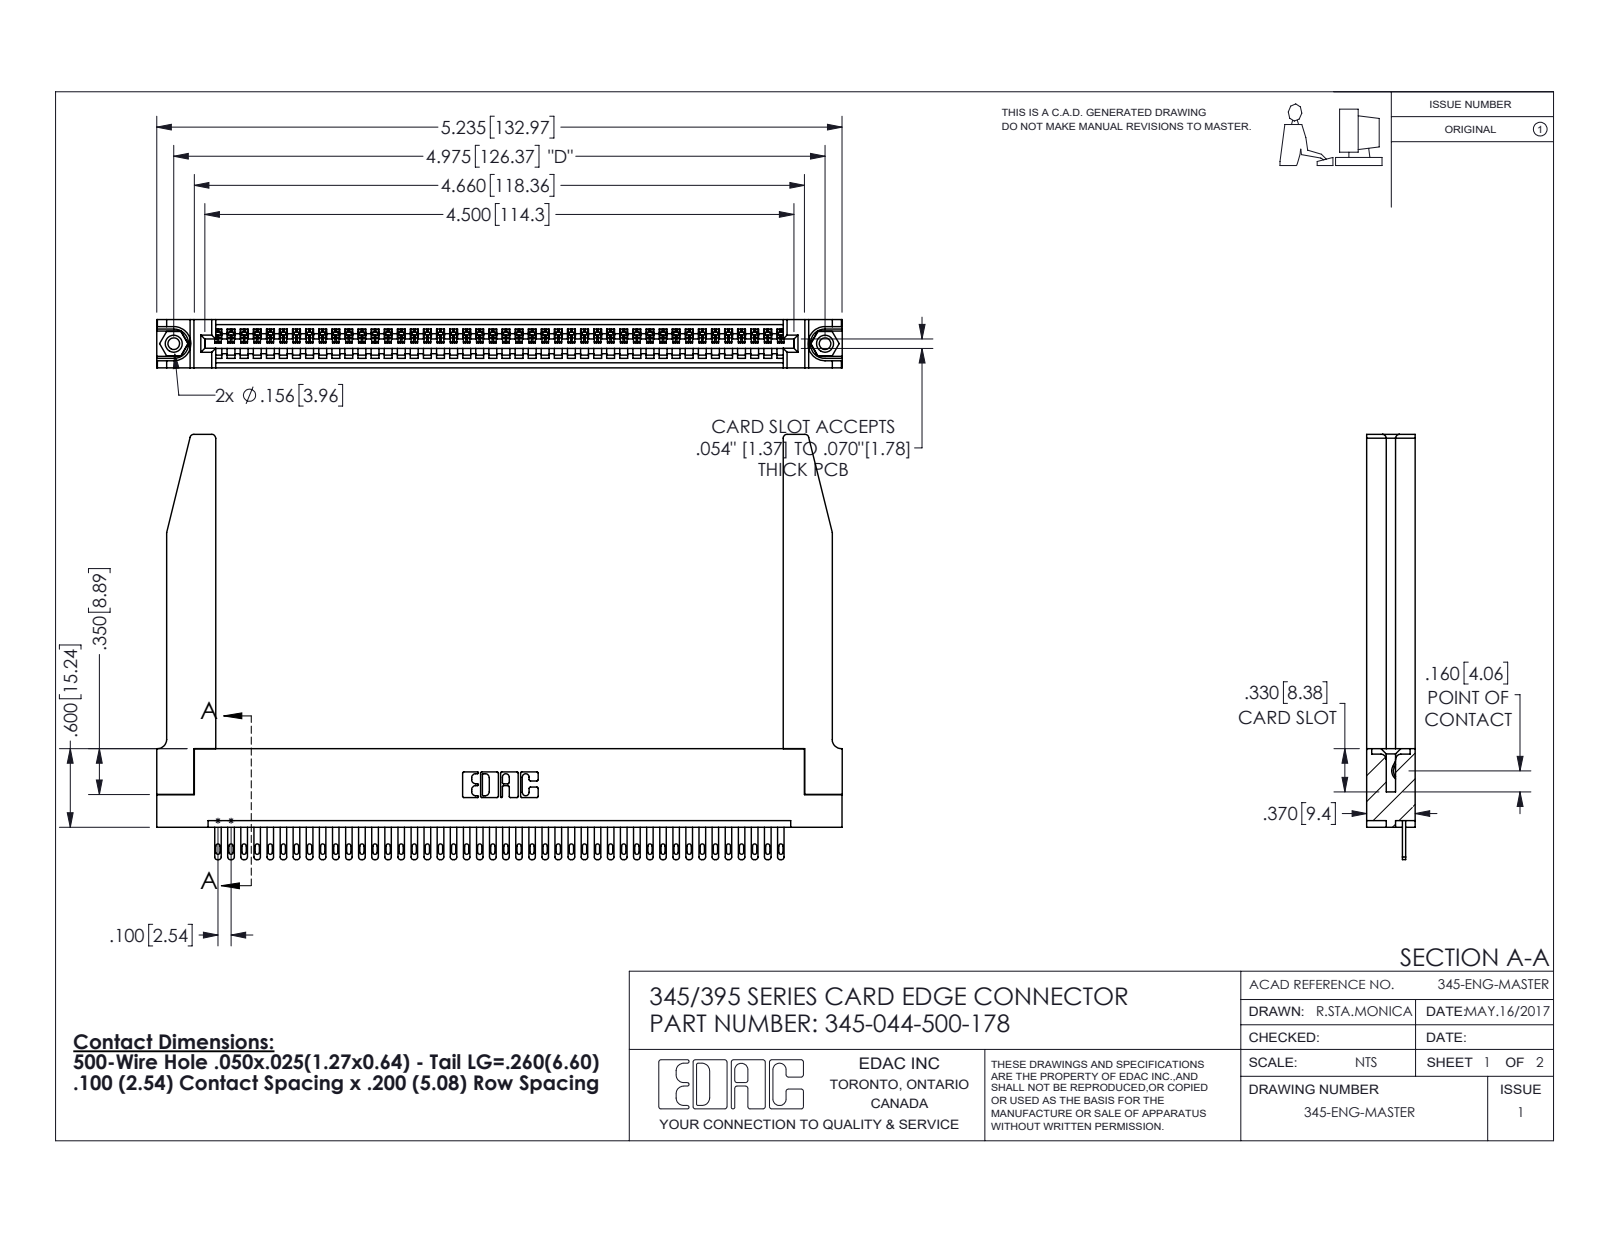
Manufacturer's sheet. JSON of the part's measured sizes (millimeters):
{"part_name": "345-250-001_345-250-001-102; 345 Part_Flush Mounting Lugs - 0.156 Dia-TH; 345-292-001_345-293-100; 345-044-500-178 (+1 more)", "step_written_by": "SolidWorks 2016 (CONFIG_CONTROL_DESIGN)", "units": "millimeters", "bodies": {"solids": 49, "faces": 2736, "planar": 1718, "cylindrical": 966, "other": 52}, "overall_size": [133, 82.5, 9.4], "volume_mm3": 20450, "surface_area_mm2": 23820, "round_holes": [[2.3, 2], [3.2, 2], [4, 2], [1.6, 1]], "round_bosses_or_shafts": [[3.9, 2]], "partial_cylinders_radius": [[0.2, 88], [0.4, 88], [0.5, 88], [0.3, 22], [0.8, 8], [0.2, 6], [0.8, 6], [0.7, 3]], "face_to_face_distances": [9.4, 1.8, 7.6, 5.1, 2.5, 6.9, 0.6, 5.7, 3.8, 3.8], "hole_center_spacings": [6.9, 120.4, 126.4]}
